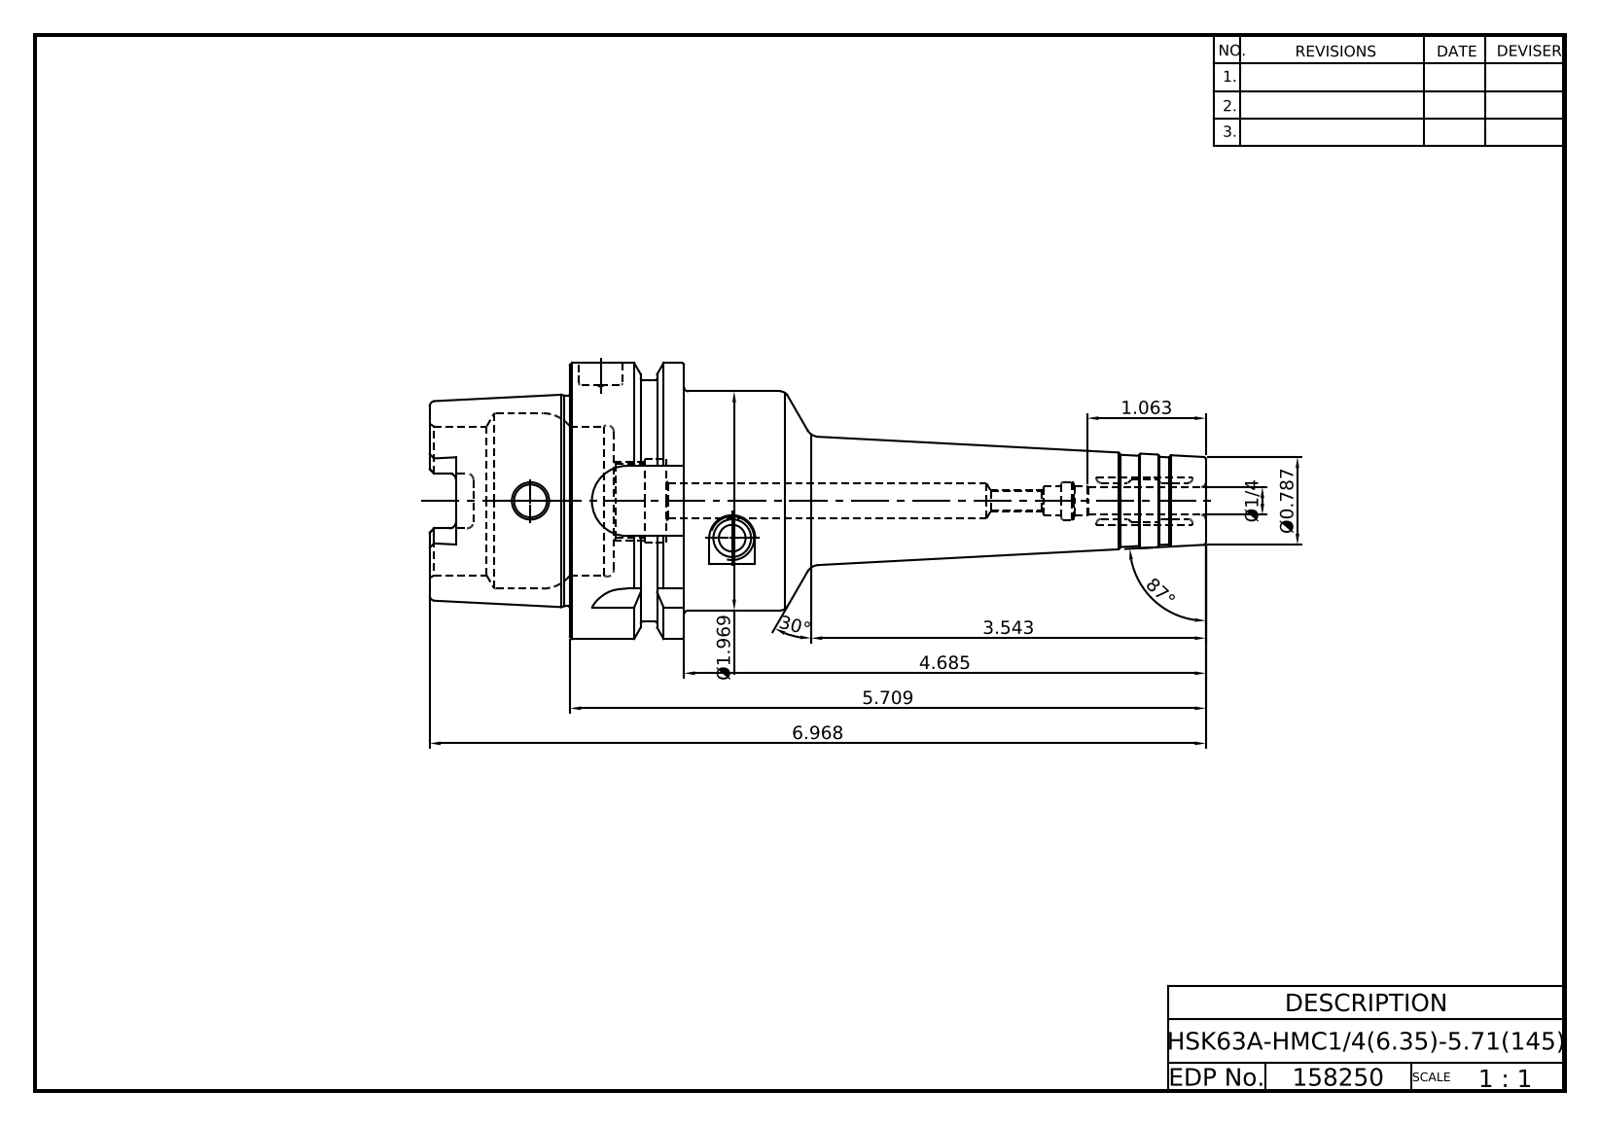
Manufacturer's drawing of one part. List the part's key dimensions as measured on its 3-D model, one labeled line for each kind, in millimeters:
Part name (STEP PRODUCT): HSK63A-HMC1_4-5_71-158250
STEP written by: PRO/ENGINEER BY PARAMETRIC TECHNOLOGY CORPORATION, 2015200 (CONFIG_CONTROL_DESIGN)
Units: millimetres
Bodies: 1 solid, 178 faces (63 planar, 47 cylindrical, 68 other)
Overall size (bounding box): 177 × 63 × 63
Volume: 176 896 mm³ · Surface area: 33 852 mm²
Round holes (diameter × count): ⌀6.35 ×1, ⌀7.5 ×1, ⌀10 ×1, ⌀10.5 ×1, ⌀17 ×1, ⌀18 ×1, ⌀19 ×1, ⌀34 ×1, ⌀40 ×1
Round bosses / shafts (diameter × count): ⌀63 ×1, ⌀55 ×1, ⌀50 ×1, ⌀48.04 ×1
Partial cylindrical surfaces — rounded edges, fillets, slot ends (radius × count): R1.5 ×6, R2.88 ×4, R8 ×4
Main face-to-face distances: 26, 10, 16, 32, 6.12, 9.88, 42, 58, 4, 22
Hole centre spacings: 46.78
